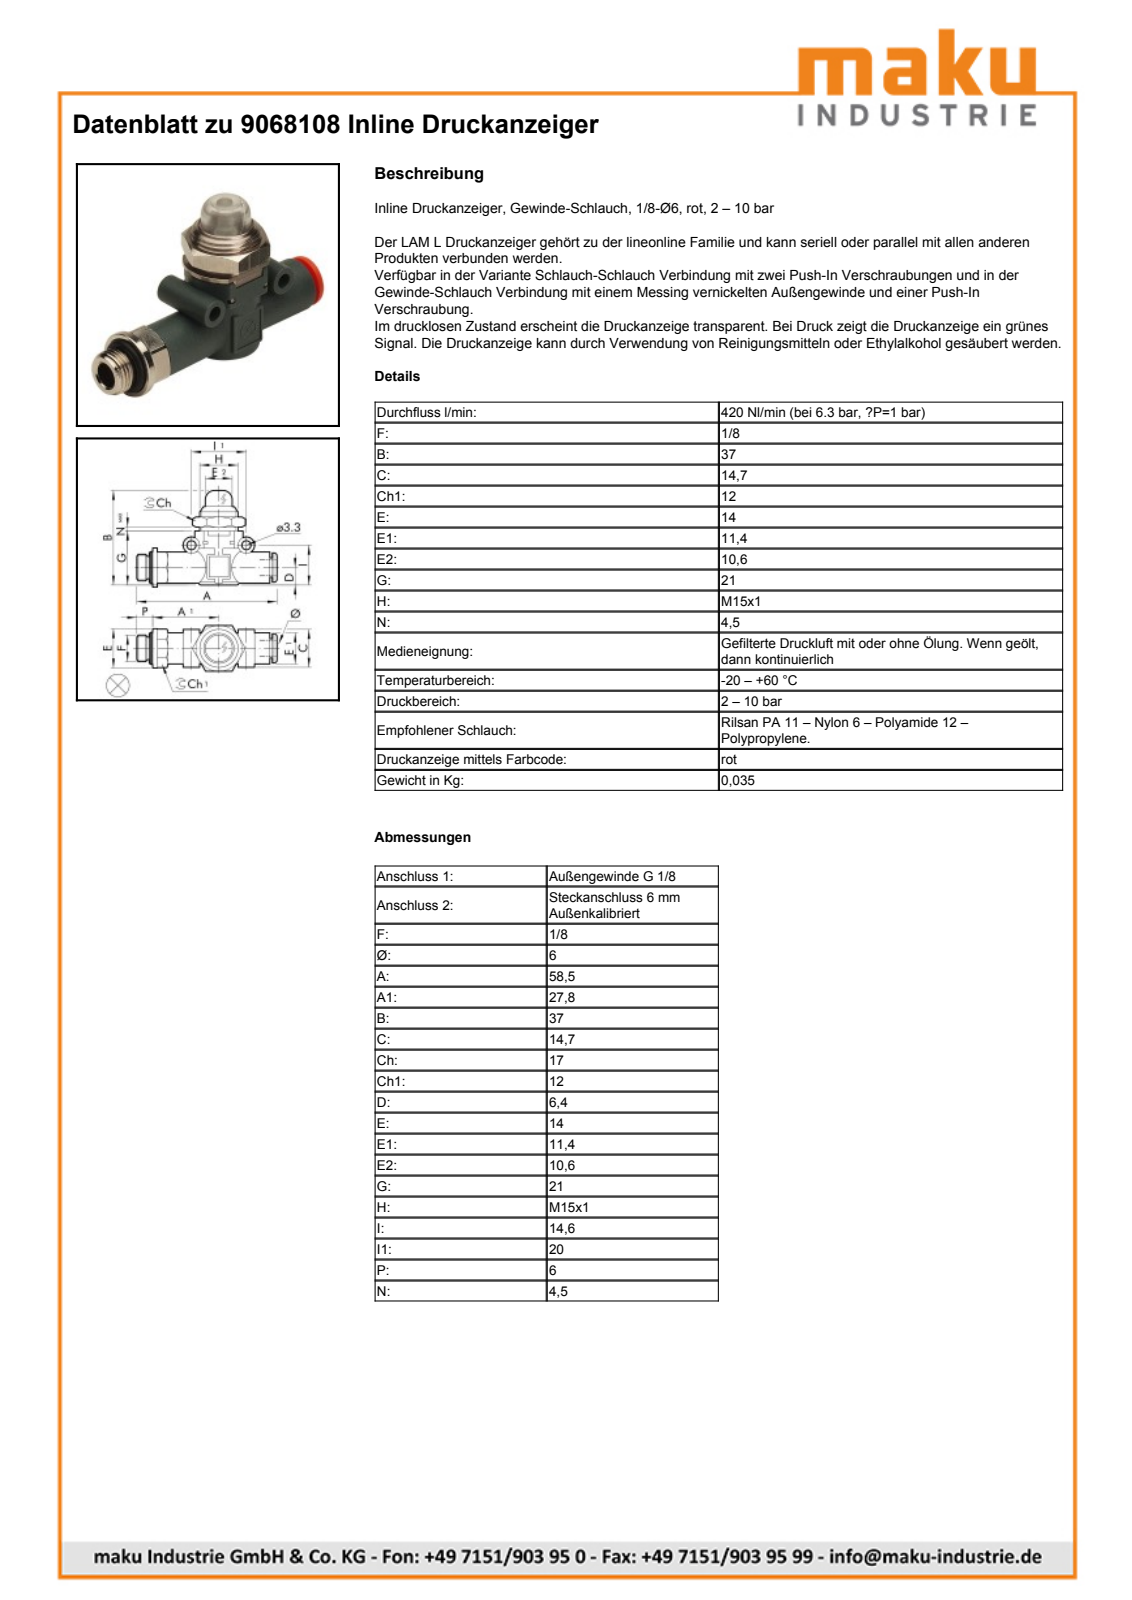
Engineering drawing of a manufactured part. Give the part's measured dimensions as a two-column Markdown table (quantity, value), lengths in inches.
| quantity | value |
| --- | --- |
| part name | 9068108; LINE-ON-LINE D6 V2v/V3V_L body; LINE-ON-LINE D6 VNR-L bushing; LINE-ON-LINE D6-1/8 thread port (+1 more) |
| STEP written by | PARTsolutions (AUTOMOTIVE_DESIGN) |
| units | inches |
| bodies | 4 solids, 201 faces (108 planar, 63 cylindrical, 30 other) |
| overall size | 2.303 × 1.48 × 0.669 |
| volume | 0.47 in³ |
| surface area | 11.75 in² |
| round holes (diameter × count) | 0.13 × 2, 0.138 × 1, 0.157 × 1, 0.197 × 1, 0.236 × 1, 0.244 × 1, 0.354 × 1, 0.378 × 1, 0.406 × 1, 0.457 × 1 |
| round bosses / shafts (diameter × count) | 0.551 × 2, 0.236 × 2, 0.583 × 1, 0.449 × 1, 0.433 × 1, 0.417 × 1, 0.383 × 1, 0.323 × 1 |
| partial cylindrical surfaces (radius × count) | 0.148 × 1, 0.27 × 1, 0.295 × 1, 0.311 × 1, 0.313 × 1, 0.358 × 1, 0.36 × 1, 0.38 × 1 |
| main face-to-face distances | 0.669, 0.049, 0.724, 0.571, 0.366, 0.659, 0.561, 0.055, 0.039, 0.11 |
| hole center spacings | 0.502, 0.787 |
